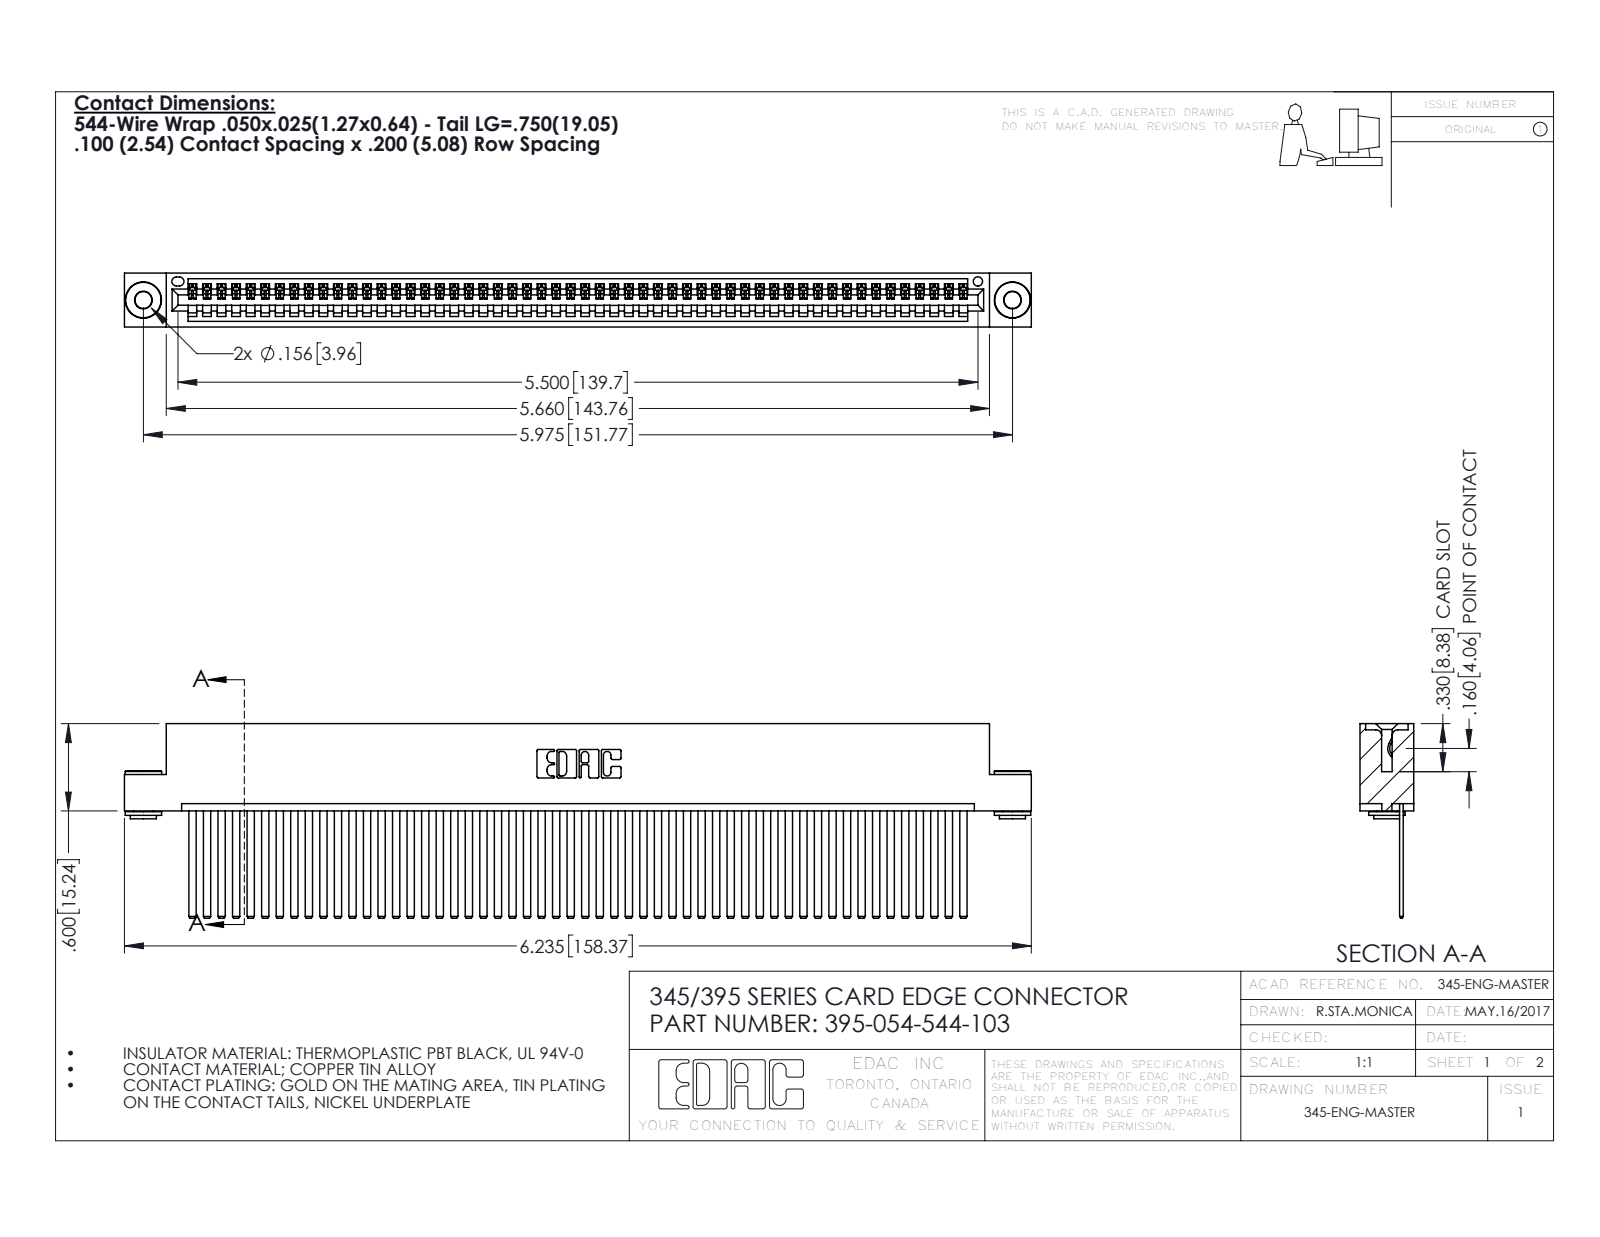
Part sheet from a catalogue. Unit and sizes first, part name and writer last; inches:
Units: inches
Overall size (bounding box): 6.235 × 1.337 × 0.37
Round holes (diameter × count): ⌀0.116 ×2, ⌀0.156 ×2, ⌀0.064 ×1
Round bosses / shafts (diameter × count): ⌀0.25 ×2, ⌀0.18 ×2, ⌀0.136 ×2
Partial cylindrical surfaces — rounded edges, fillets, slot ends (radius × count): R0.006 ×108, R0.01 ×22, R0.007 ×6, R0.031 ×6, R0.026 ×3, R0.031 ×2, R0.04 ×2, R0.014 ×1
Main face-to-face distances: 0.072, 0.298, 0.025, 0.098, 0.272, 0.37, 0.2, 0.225, 0.149, 0.072
Hole centre spacings: 0.27, 5.739, 5.975
Volume: 0.963 in³ · Surface area: 36.01 in²
Bodies: 57 solids, 2972 faces (2034 planar, 930 cylindrical, 8 other)
Part name (STEP PRODUCT): 395-054-544-103; 345-250-002_345-250-002-102; 345 Part_Flush Mounting Lugs - 0.156 Dia-TH; 345-292-001_345-293-144
STEP written by: SolidWorks 2016 (CONFIG_CONTROL_DESIGN)
